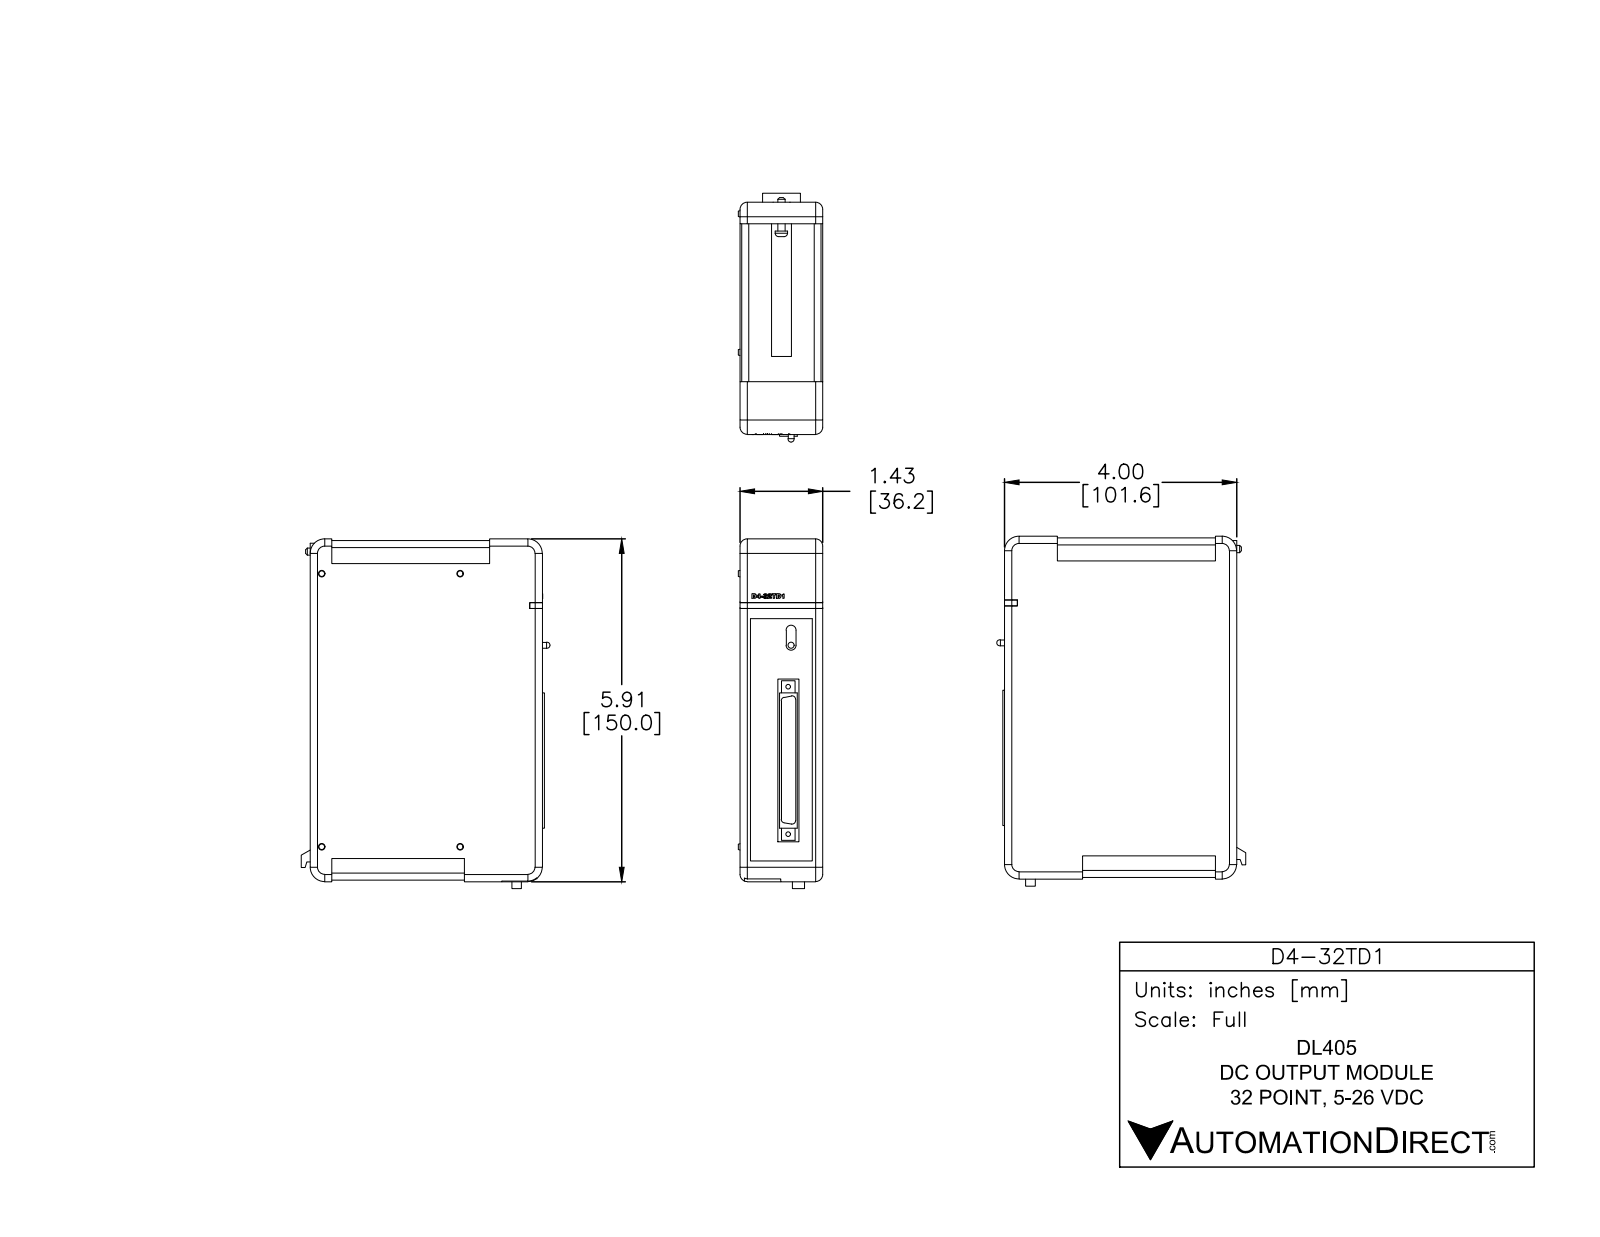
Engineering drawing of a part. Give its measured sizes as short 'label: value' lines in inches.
name: D4-32TD1
written by: SolidWorks 2014 (AUTOMOTIVE_DESIGN)
unit: in
bodies: 2 solids, 291 faces (186 planar, 46 cylindrical, 59 other)
size: 6.025 × 4.285 × 1.455
volume: 32.07 in³; area: 83.59 in²
holes: 2× ⌀0.08
bosses: 1× ⌀0.212, 1× ⌀0.123, 1× ⌀0.1
rounds: 8× R0.125, 4× R0.06, 4× R0.12, 4× R0.25, 2× R0.085, 1× R0.145, 1× R0.171
face distances: 1.425, 0.03, 3.97, 1.395, 5.845, 5.875, 4, 0.2, 3.77, 3.8
hole spacings: 2.538
